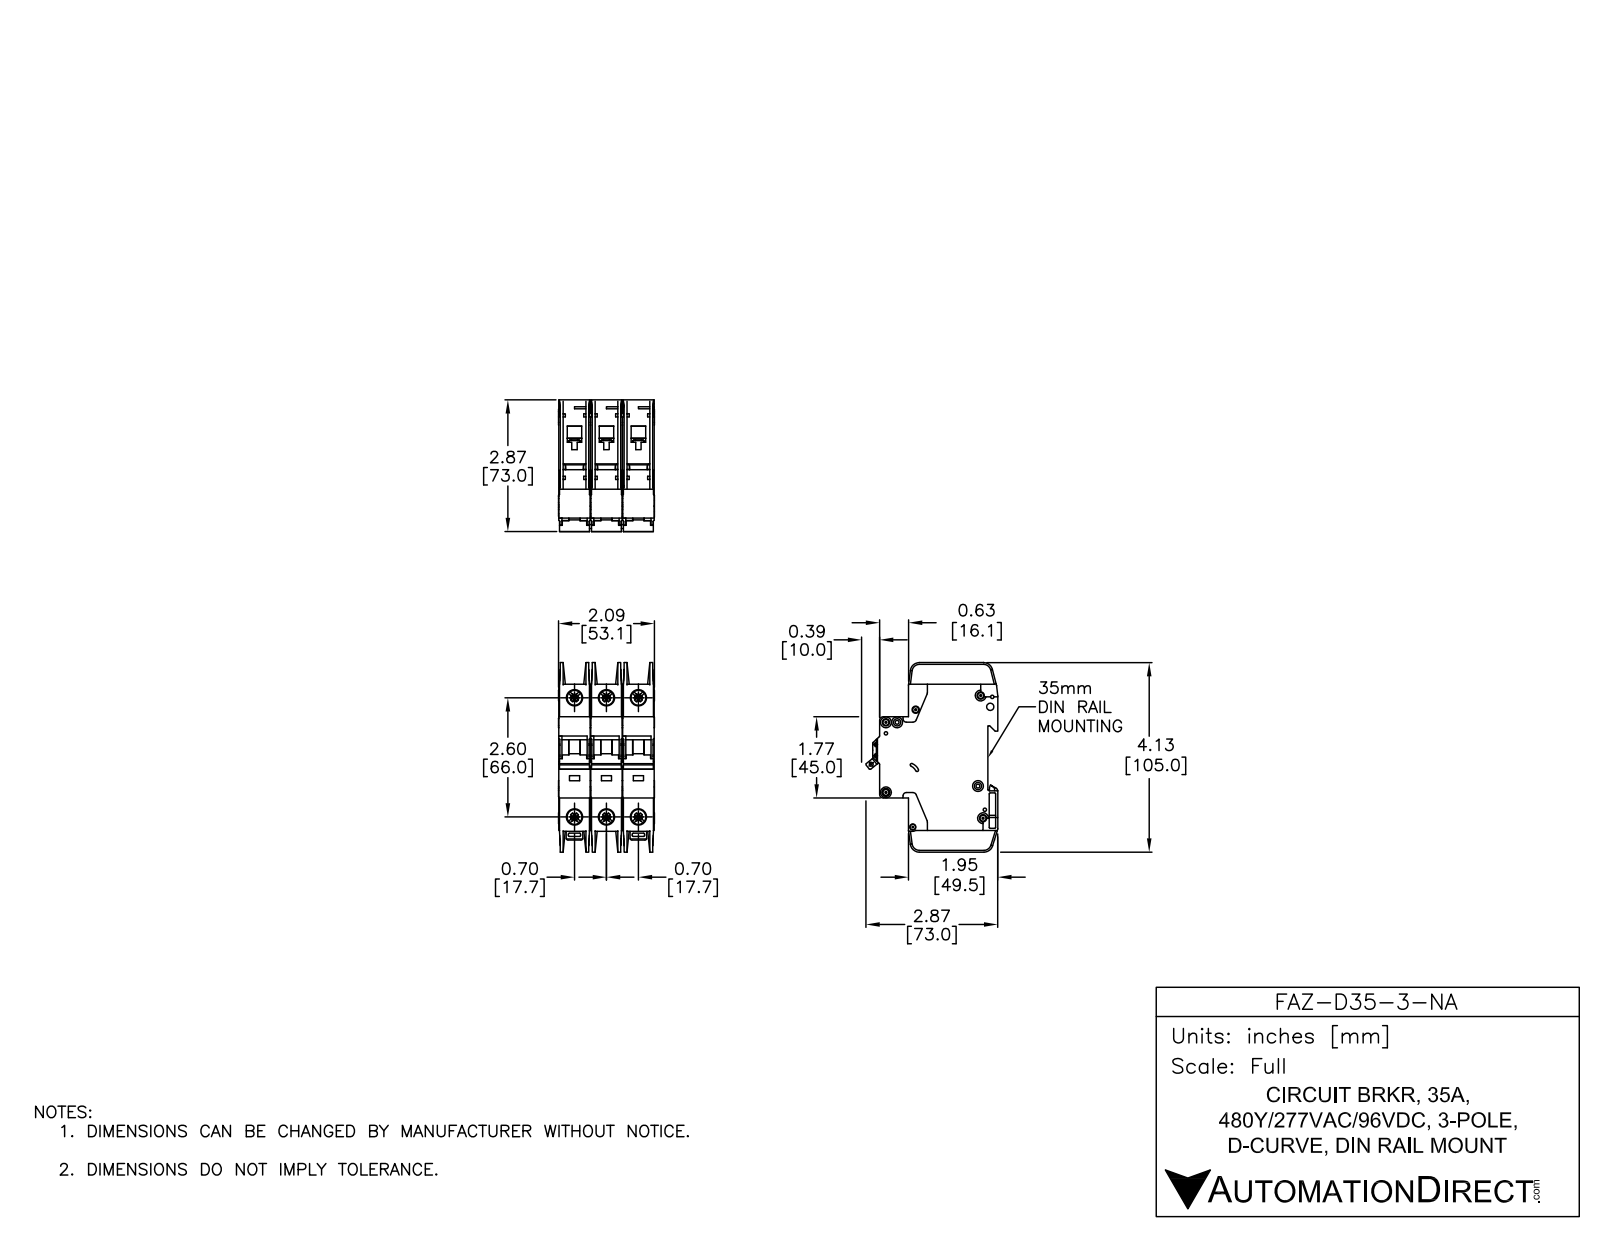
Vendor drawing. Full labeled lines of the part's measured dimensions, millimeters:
Part name (STEP PRODUCT): FAZ-D35-3-NA
STEP written by: SolidWorks 2014 (AUTOMOTIVE_DESIGN)
Units: millimetres
Bodies: 9 solids, 2352 faces (1227 planar, 789 cylindrical, 336 other)
Overall size (bounding box): 105 × 73.04 × 53.1
Volume: 233 085 mm³ · Surface area: 74 219 mm²
Round holes (diameter × count): ⌀3.6 ×7, ⌀7.15 ×6, ⌀8.2 ×6, ⌀1.09 ×2, ⌀1.5 ×2, ⌀4 ×2, ⌀1.9 ×1, ⌀2.15 ×1, ⌀2.2 ×1, ⌀2.55 ×1, ⌀3.3 ×1, ⌀3.4 ×1
Round bosses / shafts (diameter × count): ⌀6 ×7, ⌀2.5 ×3
Partial cylindrical surfaces — rounded edges, fillets, slot ends (radius × count): R0.25 ×65, R0.5 ×30, R1 ×26, R2 ×14, R1.8 ×5, R5 ×5, R4 ×4, R0.2 ×2
Main face-to-face distances: 17.7, 35.4, 17.5, 35.2, 0.7, 15.05, 2.45, 1.75, 15.75, 13.3
Hole centre spacings: 17.7, 68.33, 66, 6.2, 35.4, 74.89, 5.19, 6.1
